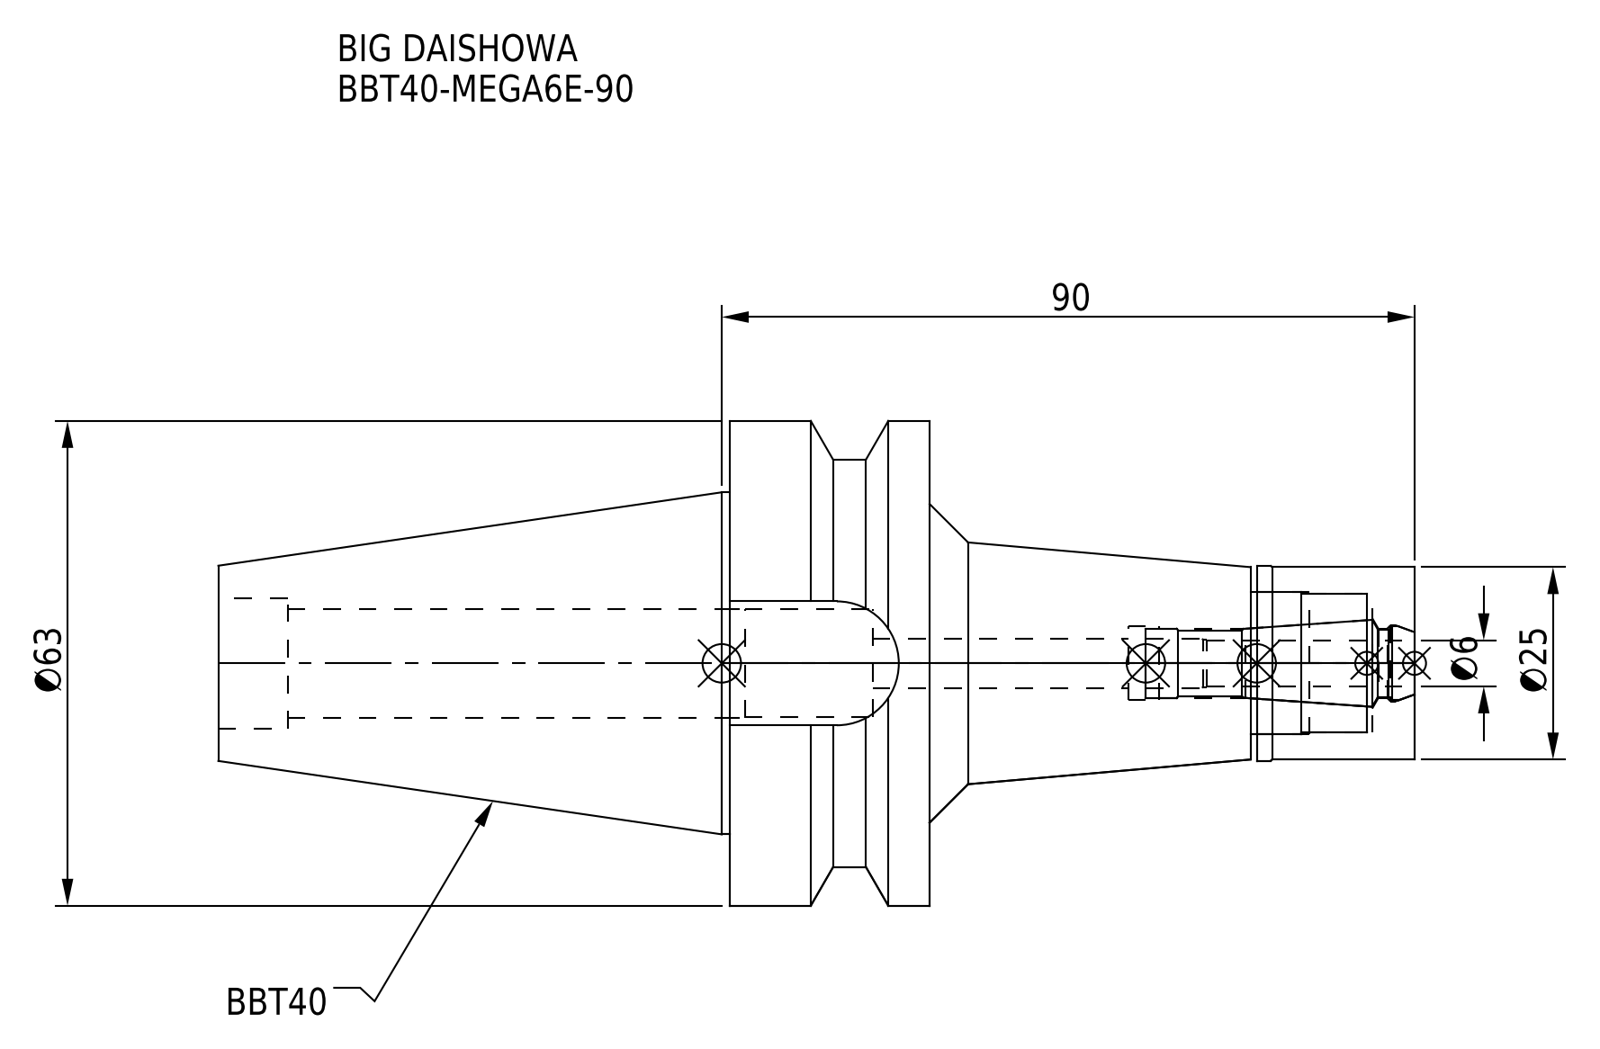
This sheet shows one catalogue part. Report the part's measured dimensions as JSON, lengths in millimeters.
{"part_name": "BBT40-MEGA6E-90-060.stp; BBT40ME06090-060_ASM.stp; BBT40-MEGA6E-90-060-FreeParts; BBT40-MEGA6E-90_1.stp (+3 more)", "step_written_by": "SolidWorks 2019 (CONFIG_CONTROL_DESIGN)", "units": "millimeters", "bodies": {"solids": 2, "faces": 81, "planar": 21, "cylindrical": 40, "other": 20}, "overall_size": [155.4, 63, 63], "volume_mm3": 156244, "surface_area_mm2": 31786, "round_holes": [[6.4, 1], [9, 1], [9.6, 1], [9.9, 1], [14, 1], [14.2, 1], [17, 1], [18, 1], [18.5, 1]], "round_bosses_or_shafts": [[63, 1], [53, 1], [44.45, 1], [25.3, 1], [25, 1]], "partial_cylinders_radius": [[8.05, 1]], "face_to_face_distances": [26, 63, 89, 45, 155.4, 92.4, 66.4, 20.5, 42.5, 68.5]}
